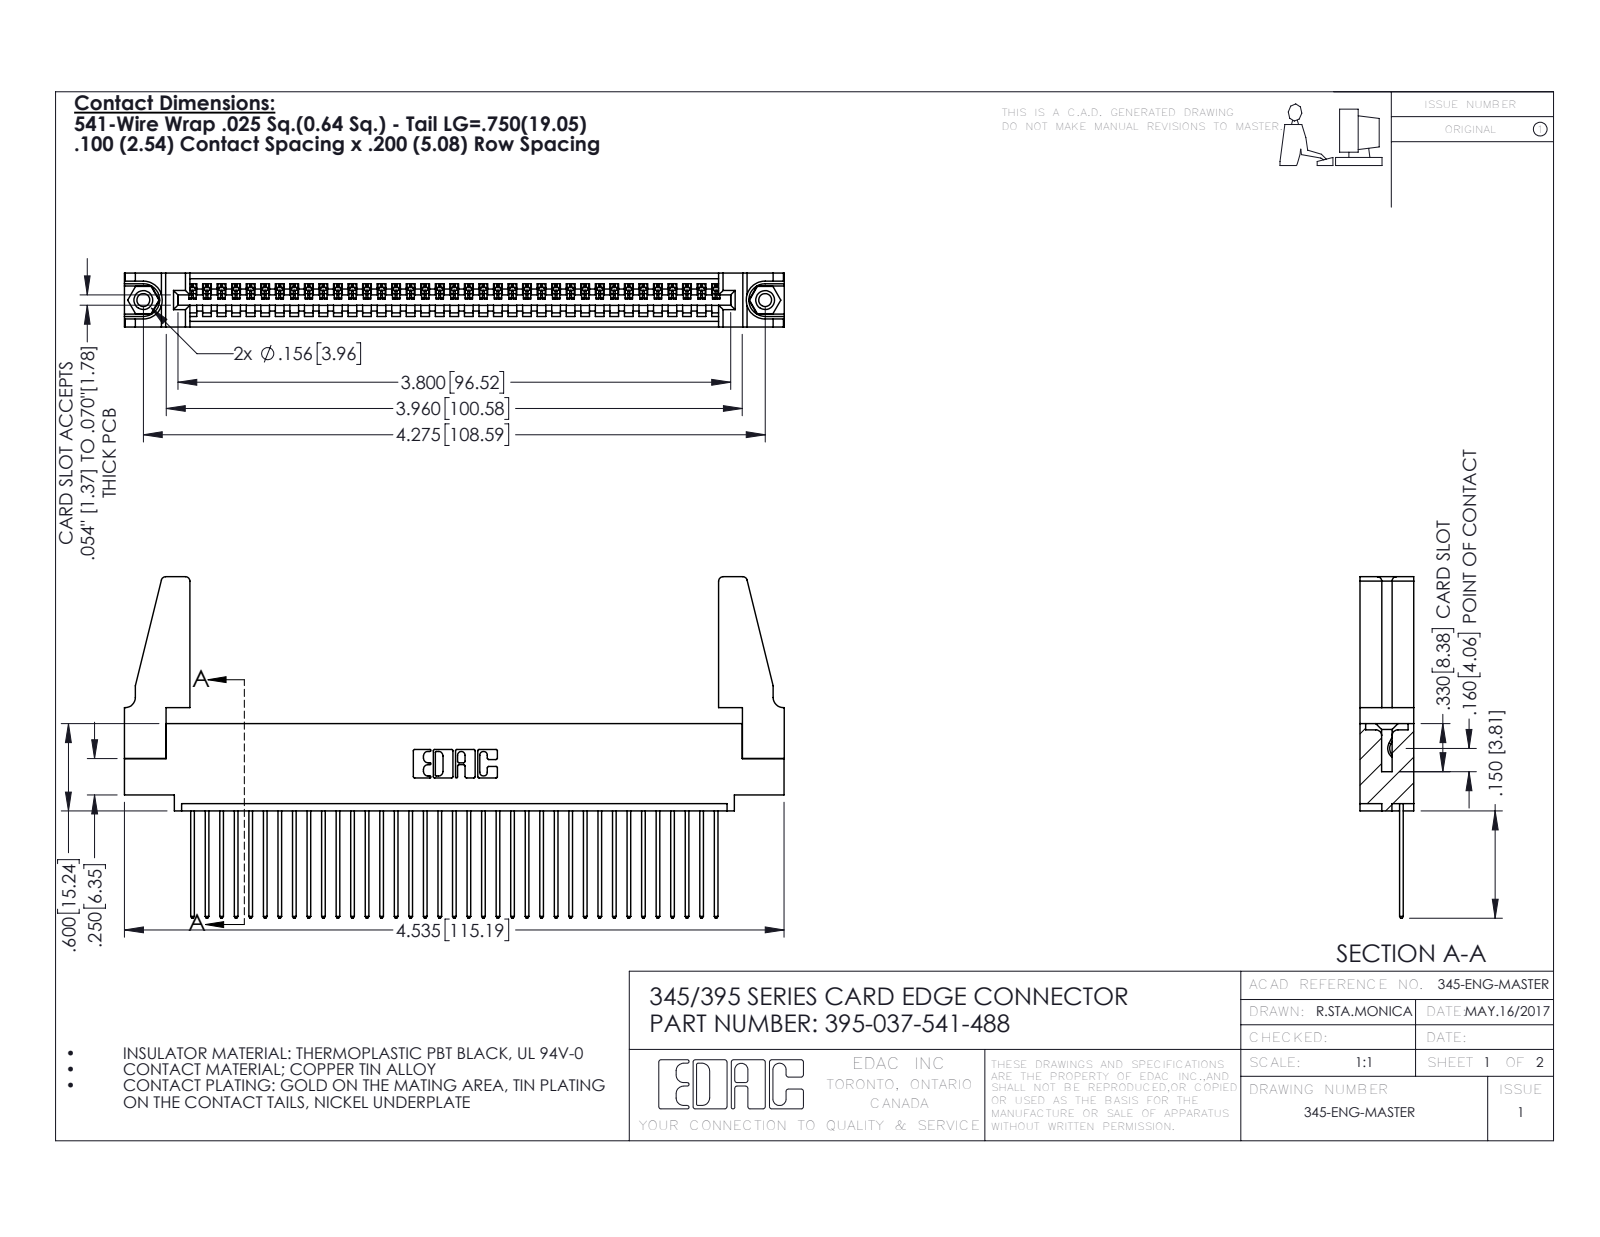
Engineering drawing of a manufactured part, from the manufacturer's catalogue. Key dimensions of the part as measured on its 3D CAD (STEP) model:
Part name (STEP PRODUCT): 345-220-078_345-220-088; 345-250-001_345-250-001-102; 345-292-001_345-293-141; 345 Part_0.110 Offset - 0.156 Dia-TH (+1 more)
STEP written by: SolidWorks 2016 (CONFIG_CONTROL_DESIGN)
Units: inches
Bodies: 42 solids, 2400 faces (1636 planar, 748 cylindrical, 16 other)
Overall size (bounding box): 4.536 × 2.347 × 0.37
Volume: 0.867 in³ · Surface area: 28.54 in²
Round holes (diameter × count): ⌀0.089 ×2, ⌀0.125 ×2, ⌀0.156 ×2, ⌀0.064 ×1
Round bosses / shafts (diameter × count): ⌀0.155 ×2
Partial cylindrical surfaces — rounded edges, fillets, slot ends (radius × count): R0.006 ×74, R0.01 ×74, R0.01 ×22, R0.03 ×8, R0.007 ×6, R0.031 ×6, R0.026 ×3, R0.031 ×2
Main face-to-face distances: 0.072, 0.298, 0.37, 0.098, 0.272, 0.025, 0.2, 0.225, 0.149, 0.072
Hole centre spacings: 0.27, 4.039, 4.275
